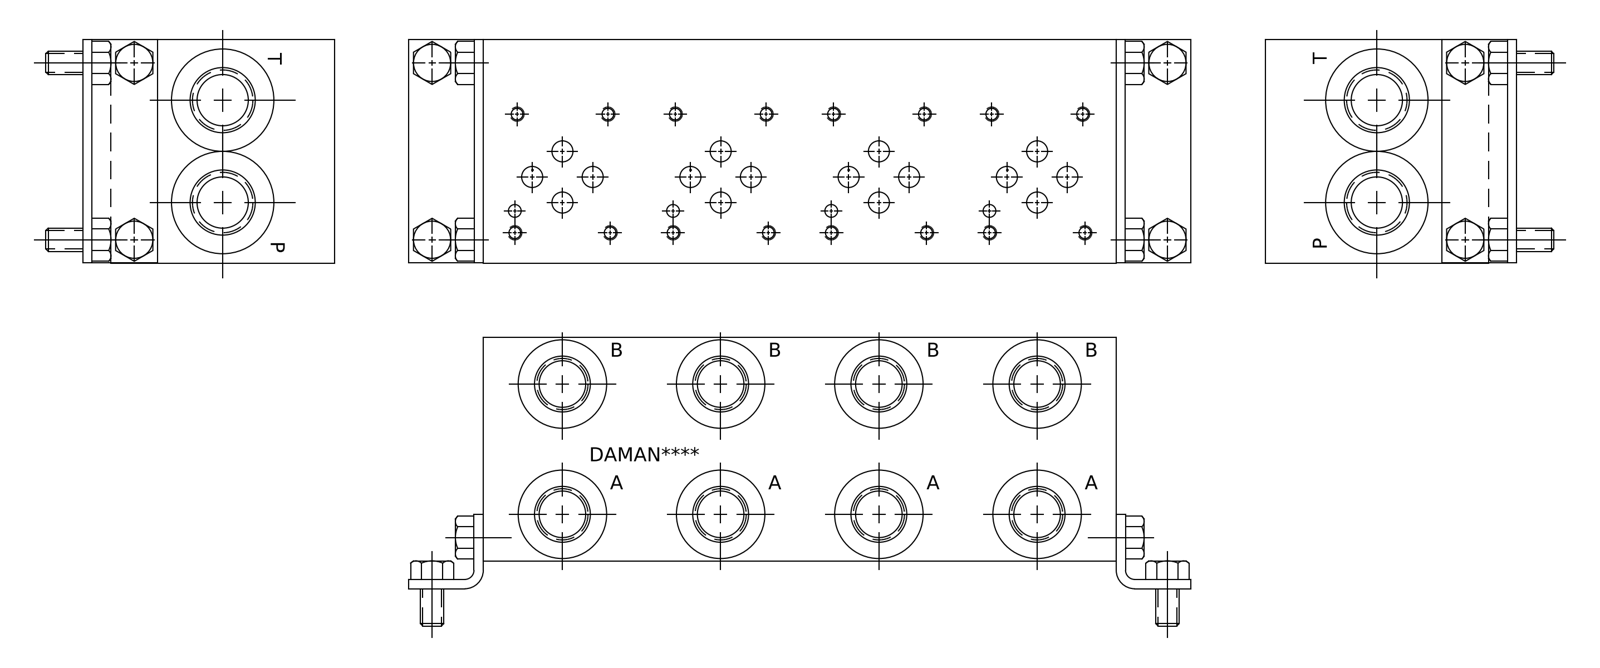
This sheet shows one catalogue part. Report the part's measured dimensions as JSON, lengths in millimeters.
{"part_name": "C:\\\\Program Files\\\\PARO\\\\Hydroman 800\\\\Export\\\\AD03P042S_PA", "step_written_by": "Autodesk Inventor 2012 (AUTOMOTIVE_DESIGN)", "units": "millimeters", "bodies": {"solids": 1, "faces": 182, "planar": 30, "cylindrical": 88, "other": 64}, "overall_size": [215.9, 76.2, 76.2], "volume_mm3": 1161000, "surface_area_mm2": 100745, "round_holes": [[3.78, 16], [7.14, 12], [14.3, 8], [17.5, 8], [20.6, 8], [30.25, 8], [3.96, 4], [6.35, 4], [6.53, 2], [15.88, 2], [20.45, 2], [23.9, 2]], "face_to_face_distances": [76.2, 0.79, 215.9, 75.41, 215.11, 3.28, 2.49, 214.32, 72.92, 212.62], "hole_center_spacings": [53.98, 107.95, 53.97, 19.95, 22.05, 33.55, 40.49, 51.45]}
